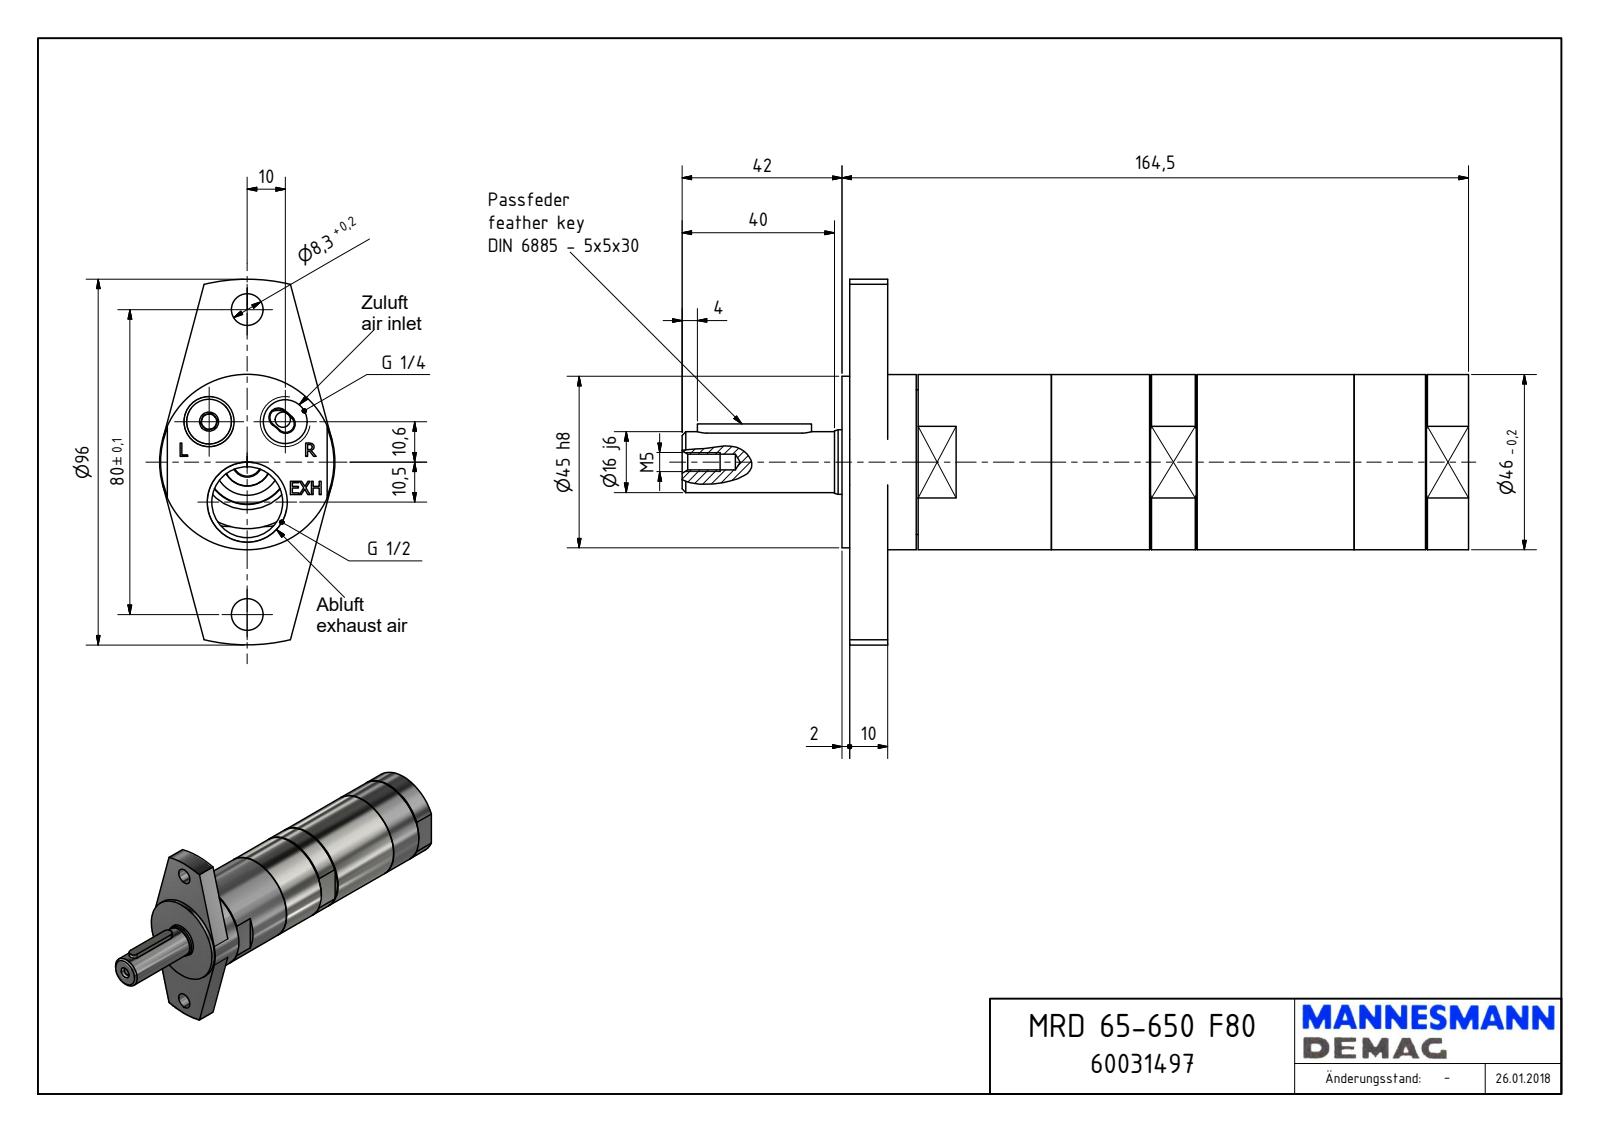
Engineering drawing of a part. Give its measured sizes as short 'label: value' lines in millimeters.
name: MRD 65-650 F80_60031497
written by: Autodesk Inventor 2018 (AUTOMOTIVE_DESIGN)
unit: mm
bodies: 1 solid, 418 faces (194 planar, 194 cylindrical, 30 other)
size: 206.5 × 96 × 46
volume: 290 301 mm³; area: 47 118 mm²
holes: 2× ⌀8.3, 1× ⌀4, 1× ⌀4.13, 1× ⌀11.45, 1× ⌀17.5, 1× ⌀18.63, 1× ⌀38, 1× ⌀38.38, 1× ⌀41, 1× ⌀42
bosses: 1× ⌀46, 1× ⌀45, 1× ⌀40.7, 1× ⌀33.28, 1× ⌀16.95, 1× ⌀16
rounds: 78× R2.8, 2× R2.5, 2× R5, 1× R5.72, 1× R16.46, 1× R16.6, 1× R48
face distances: 10, 12, 2, 152.5, 164.5, 162.5, 42, 144.5, 8, 18
hole spacings: 14.57, 23.35, 31.05, 40, 51.58, 10.5, 20, 29.5
